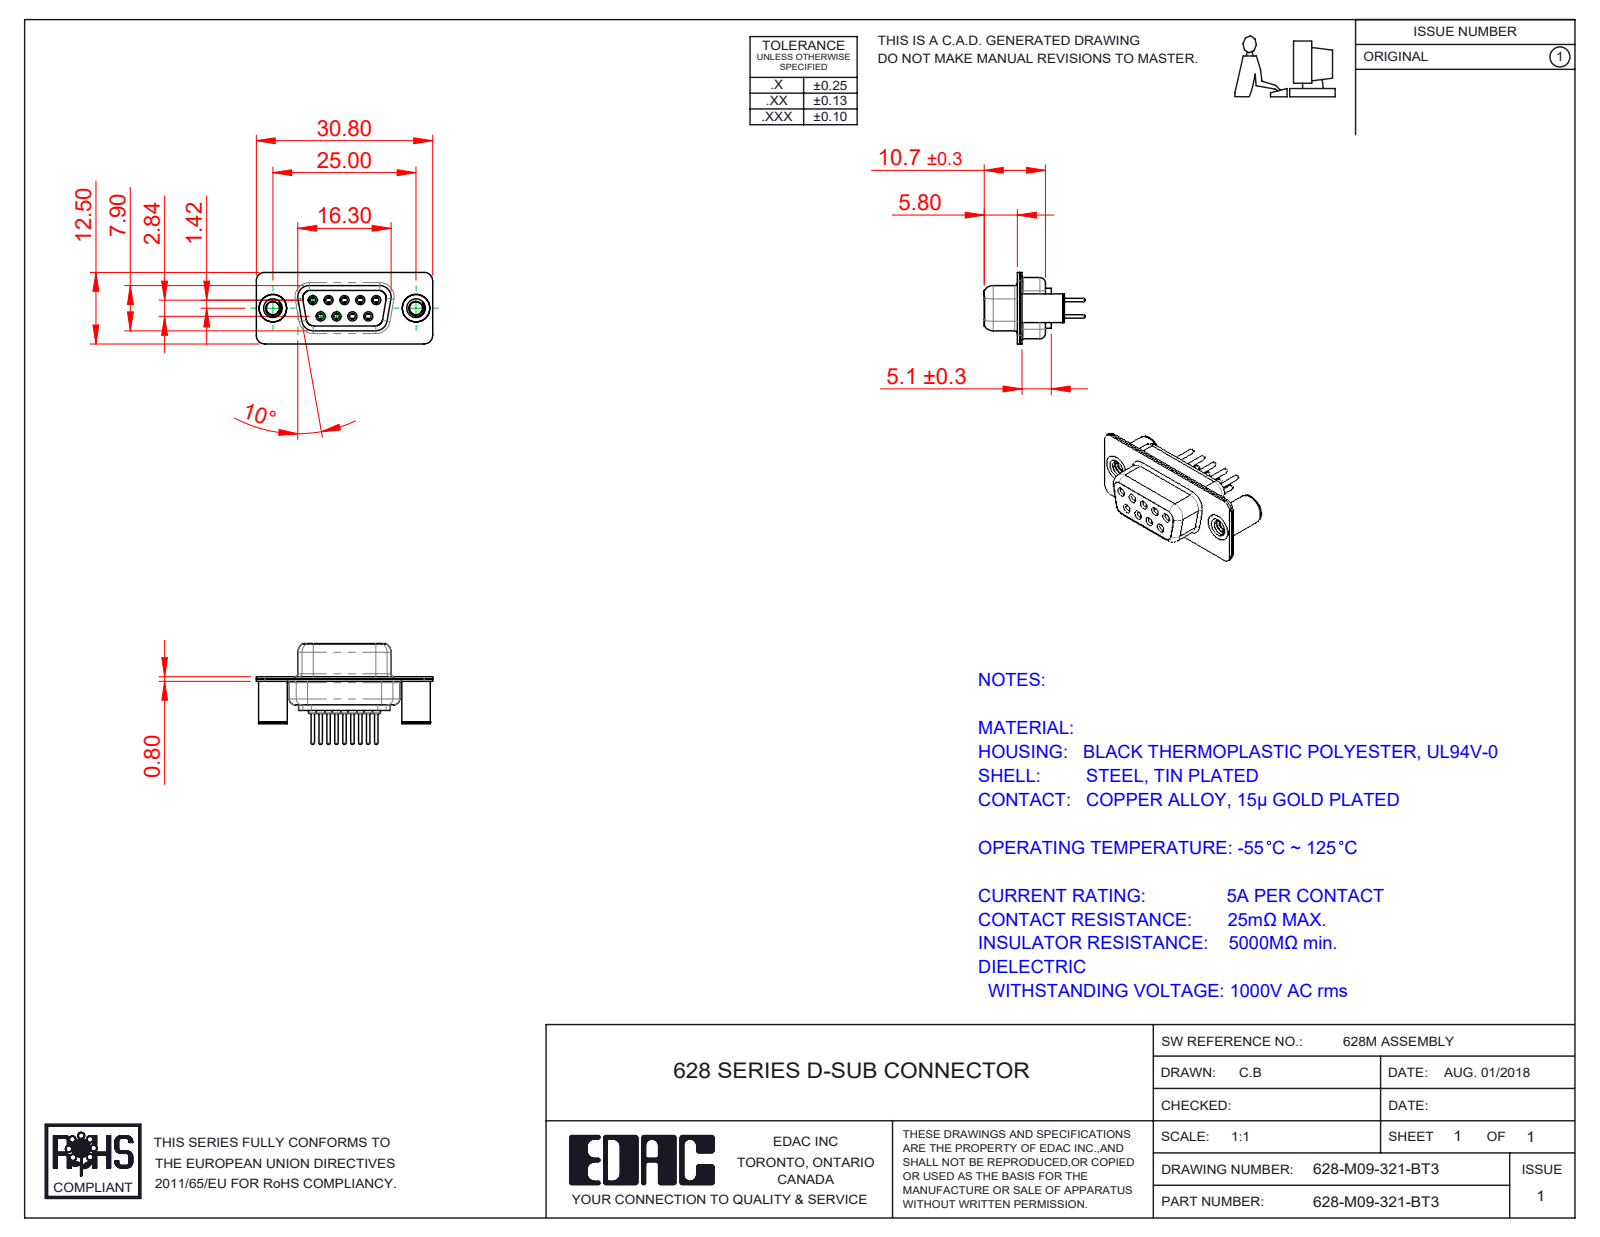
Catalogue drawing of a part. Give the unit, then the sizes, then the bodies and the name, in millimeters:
Units: millimetres
Overall size (bounding box): 30.8 × 17.6 × 12.5
Round holes (diameter × count): ⌀1 ×9, ⌀1.1 ×9, ⌀1.7 ×9, ⌀1.8 ×9, ⌀2 ×9, ⌀2.26 ×2, ⌀3.26 ×2, ⌀4 ×2, ⌀4.8 ×2
Round bosses / shafts (diameter × count): ⌀2.2 ×9, ⌀1.6 ×9, ⌀1.5 ×9, ⌀0.6 ×9, ⌀5 ×2, ⌀4.9 ×2
Partial cylindrical surfaces — rounded edges, fillets, slot ends (radius × count): R1.5 ×16, R2 ×12, R1.35 ×8, R1.6 ×8, R0.25 ×4, R0.5 ×4, R0.6 ×4, R0.65 ×4
Main face-to-face distances: 0.4, 1.4, 0.45, 8.45, 0.8, 1.8, 8.9, 1, 6.2, 7.05
Hole centre spacings: 3.16, 2.77, 5.54, 5.03, 5.04, 8.31, 7.1, 7.48
Volume: 1 825 mm³ · Surface area: 4 681 mm²
Bodies: 14 solids, 808 faces (202 planar, 332 cylindrical, 274 other)
Part name (STEP PRODUCT): 628M Housing_09 Contacts; 628M 4-40 Threaded Board Spacer; 628M Shell Front_09 Contacts; 628-M09-321-BT3 (+3 more)
STEP written by: SolidWorks 2020 (CONFIG_CONTROL_DESIGN)
